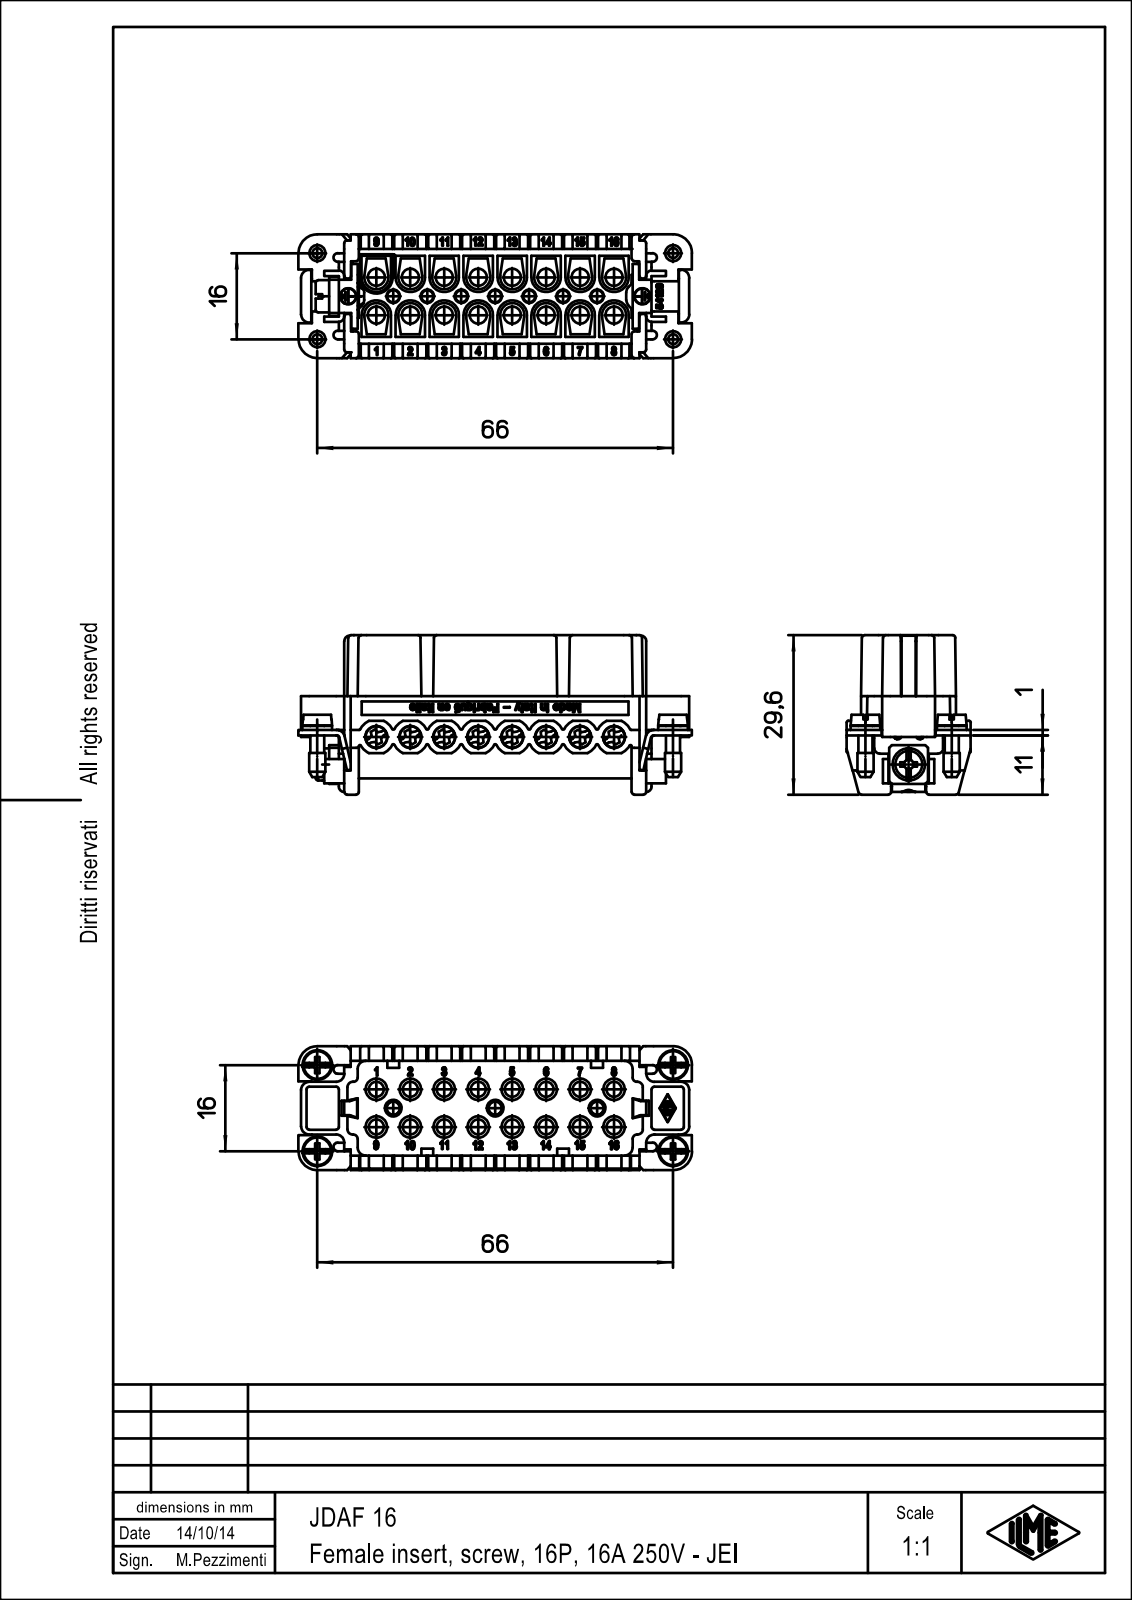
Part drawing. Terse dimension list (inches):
name: JDAF_16
written by: PTC Creo Elements/Direct Modeling 19.0B 21-Mar-2015 (C) Parametric Technology GmbH (AUTOMOTIVE_DESIGN)
unit: in
bodies: 1 solid, 2115 faces (1248 planar, 537 cylindrical, 330 other)
size: 2.874 × 1.165 × 0.906
volume: 1.497 in³; area: 24.5 in²
holes: 16× ⌀0.11, 16× ⌀0.126, 8× ⌀0.161, 4× ⌀0.118, 1× ⌀0.071
bosses: 8× ⌀0.118, 4× ⌀0.217, 4× ⌀0.102, 2× ⌀0.177, 1× ⌀0.236, 1× ⌀0.138
rounds: 60× R0.02, 26× R0.012, 20× R0.008, 20× R0.059, 15× R0.089, 14× R0.039, 8× R0.031, 8× R0.13
face distances: 0.106, 0.693, 0.245, 0.039, 0.799, 0.787, 0.069, 0.15, 0.248, 0.11
hole spacings: 0.248, 0.496, 0.744, 0.371, 0.567, 0.992, 0.793, 1.24
